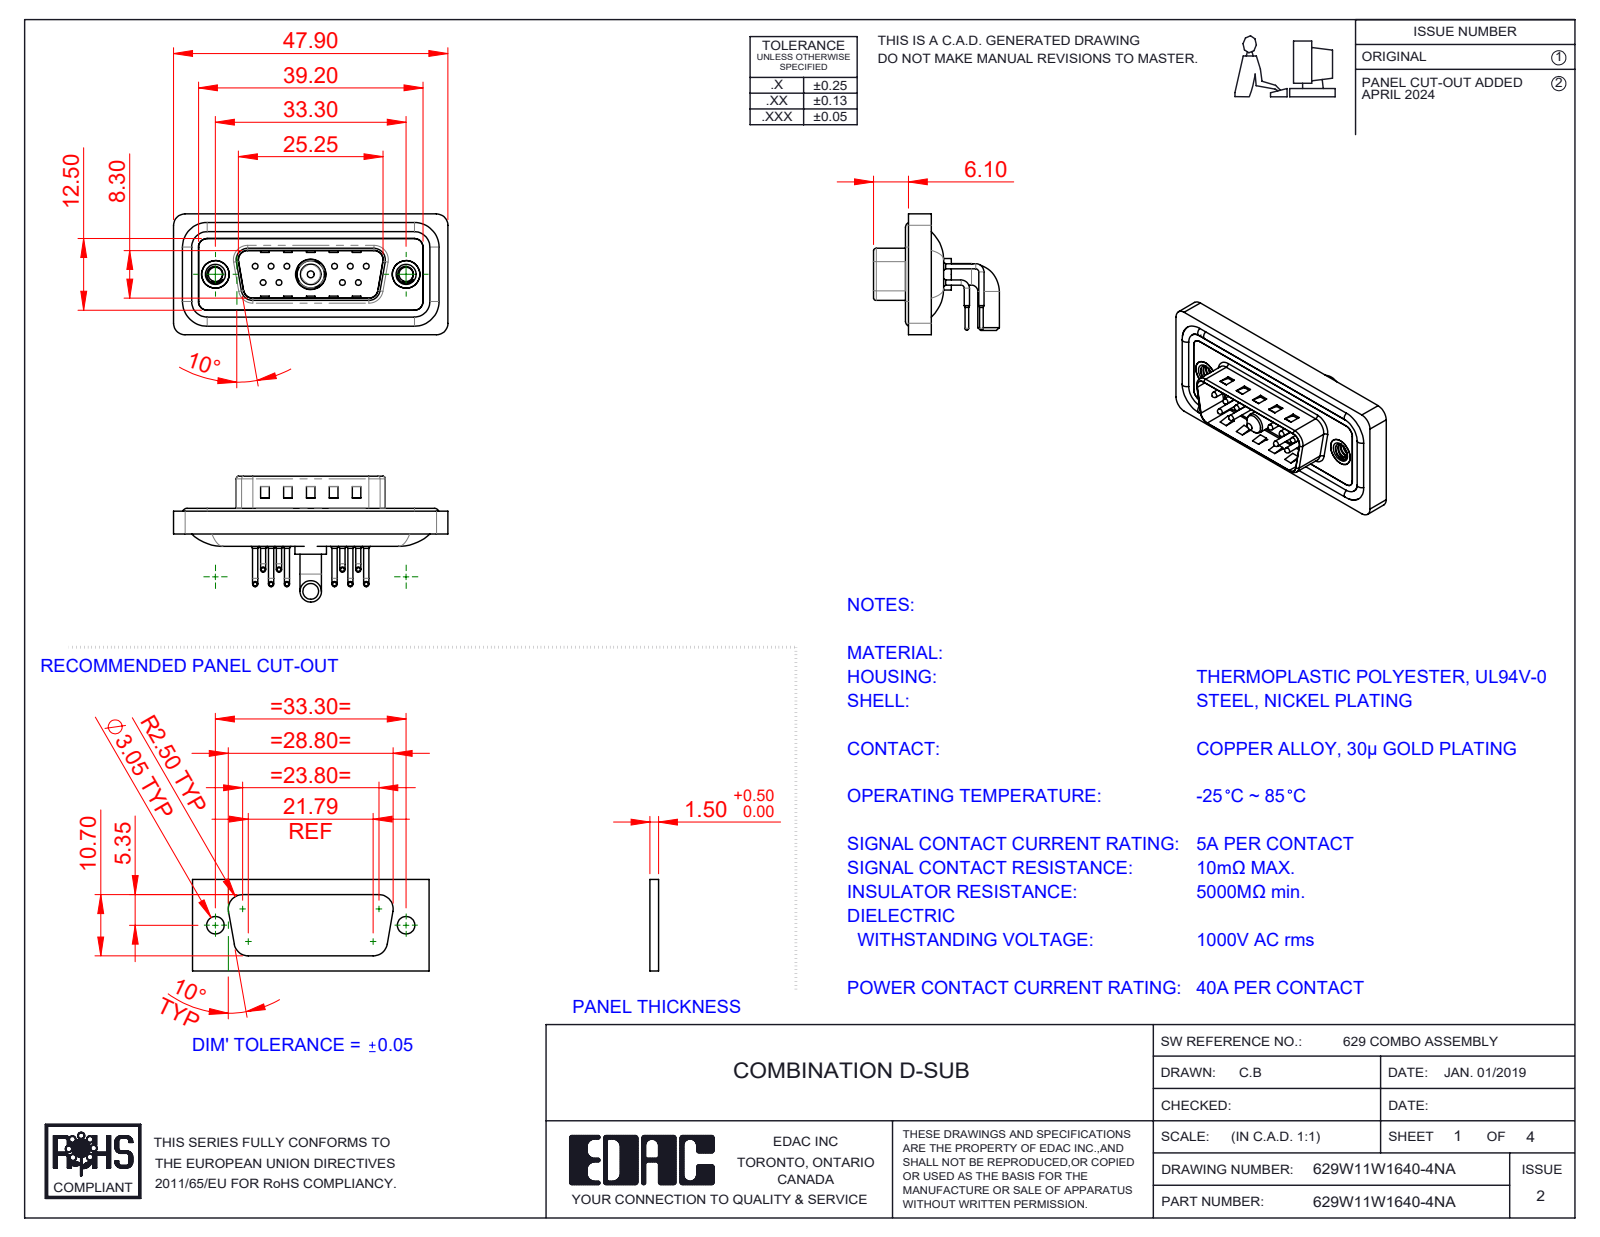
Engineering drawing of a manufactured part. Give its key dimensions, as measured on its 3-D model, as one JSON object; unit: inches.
{"part_name": "629Combo Contact Row 1; 629Combo Contact Row 2; Power Pin_40A RA; 629W11W1640-4NA (+5 more)", "step_written_by": "SolidWorks 2023 (CONFIG_CONTROL_DESIGN)", "units": "inches", "bodies": {"solids": 19, "faces": 1597, "planar": 836, "cylindrical": 567, "other": 194}, "overall_size": [1.886, 0.865, 0.831], "volume_in3": 0.346, "surface_area_in2": 14.46, "round_holes": [[0.03, 10], [0.063, 10], [0.079, 10], [0.098, 2], [0.157, 2], [0.189, 2], [0.197, 2], [0.191, 1], [0.209, 1]], "round_bosses_or_shafts": [[0.035, 20], [0.059, 10], [0.039, 10], [0.026, 10], [0.063, 4], [0.193, 2], [0.148, 2], [0.217, 1]], "partial_cylinders_radius": [[0.079, 20], [0.059, 18], [0.04, 10], [0.02, 8], [0.063, 8], [0.039, 7], [0.01, 4], [0.024, 4]], "face_to_face_distances": [0.016, 0.114, 0.031, 0.043, 0.083, 0.063, 0.098, 0.161, 0.177, 0.122], "hole_center_spacings": [0.124, 0.109, 0.545, 0.436, 0.654, 0.198, 0.198, 0.218]}
